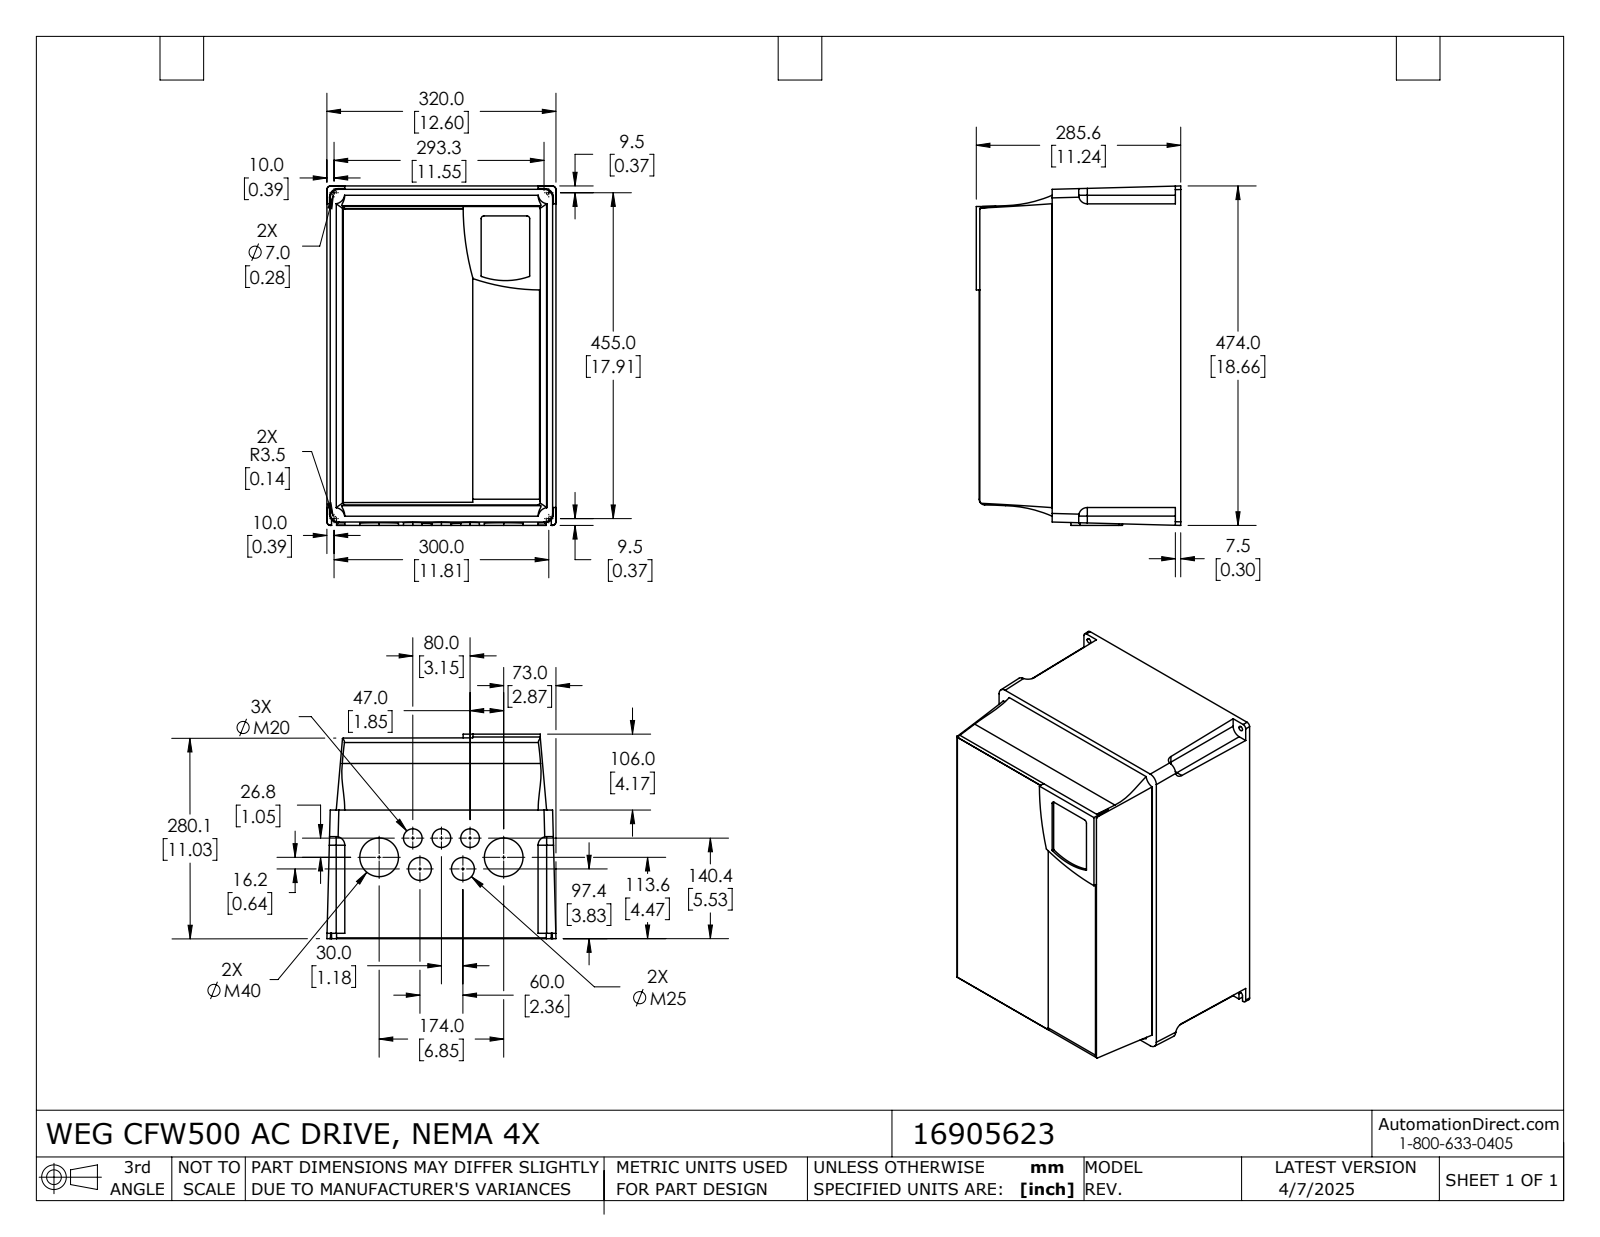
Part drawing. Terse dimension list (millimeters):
name: 16905623
written by: SolidWorks 2021 (AUTOMOTIVE_DESIGN)
unit: mm
bodies: 1 solid, 121 faces (56 planar, 57 cylindrical, 8 other)
size: 474 × 320 × 285.6
volume: 38 610 000 mm³; area: 709 700 mm²
holes: 2× ⌀7
bosses: 3× ⌀26.1, 2× ⌀54.1, 2× ⌀32.1
rounds: 12× R12, 4× R5, 2× R0.8, 2× R1, 2× R3.5, 2× R3.9, 1× R0.5, 1× R2.9
face distances: 281.6, 179.6, 102, 282.6, 103, 1, 3, 285.6, 106, 4
hole spacings: 300
